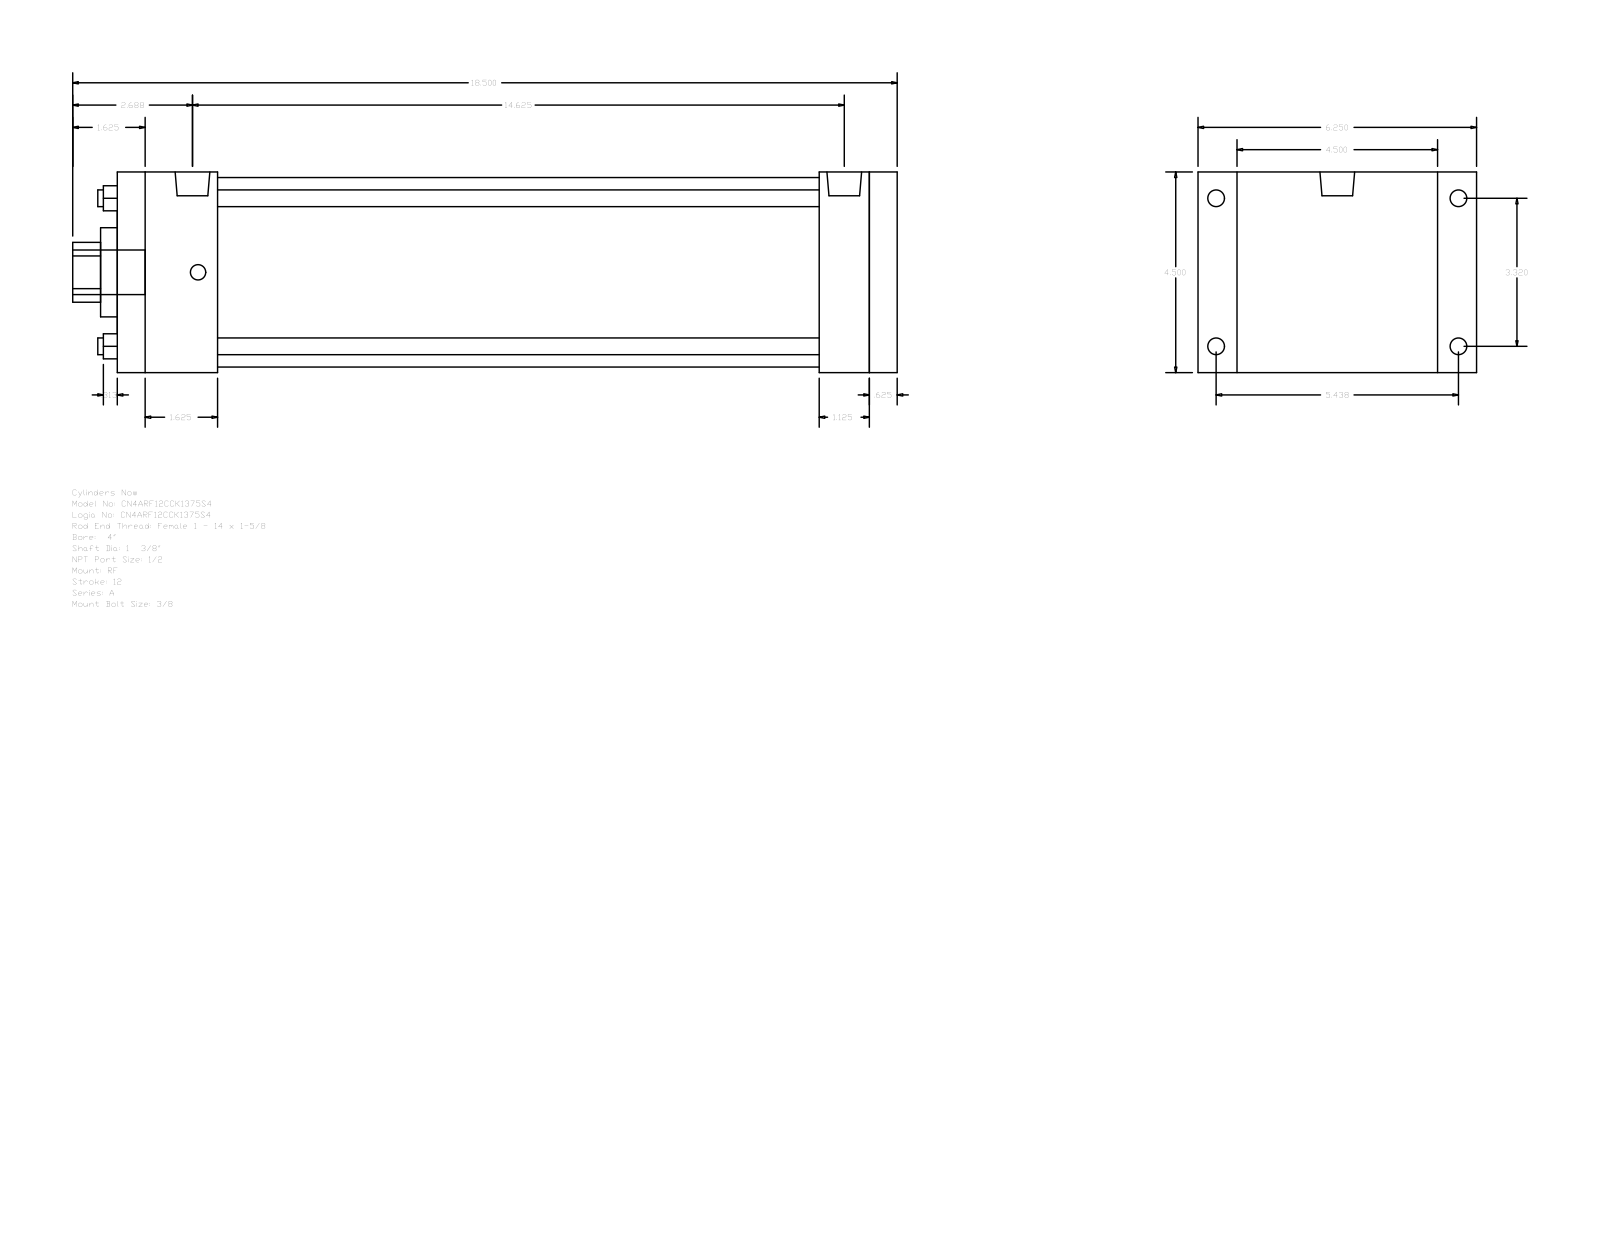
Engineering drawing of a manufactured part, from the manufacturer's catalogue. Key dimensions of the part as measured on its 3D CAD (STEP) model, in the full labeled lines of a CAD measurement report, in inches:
Part name (STEP PRODUCT): A_RF__0400_1.375
STEP written by: GSSL Pune (CONFIG_CONTROL_DESIGN)
Units: inches
Bodies: 0 solids, 92 faces (64 planar, 28 cylindrical, 0 other)
Overall size (bounding box): 18.5 × 6.25 × 4.5
Round holes (diameter × count): ⌀0.375 ×4, ⌀1.375 ×1, ⌀2 ×1, ⌀4.25 ×1
Round bosses / shafts (diameter × count): ⌀0.375 ×4, ⌀0.344 ×4, ⌀0.778 ×2, ⌀1 ×1
Partial cylindrical surfaces — rounded edges, fillets, slot ends (radius × count): R0.672 ×1
Main face-to-face distances: 4.5, 17.5, 0.625, 16.875, 1.125, 0.875, 5.375, 15.75, 1.75, 2.25
Hole centre spacings: 2.347, 3.32, 4.695
